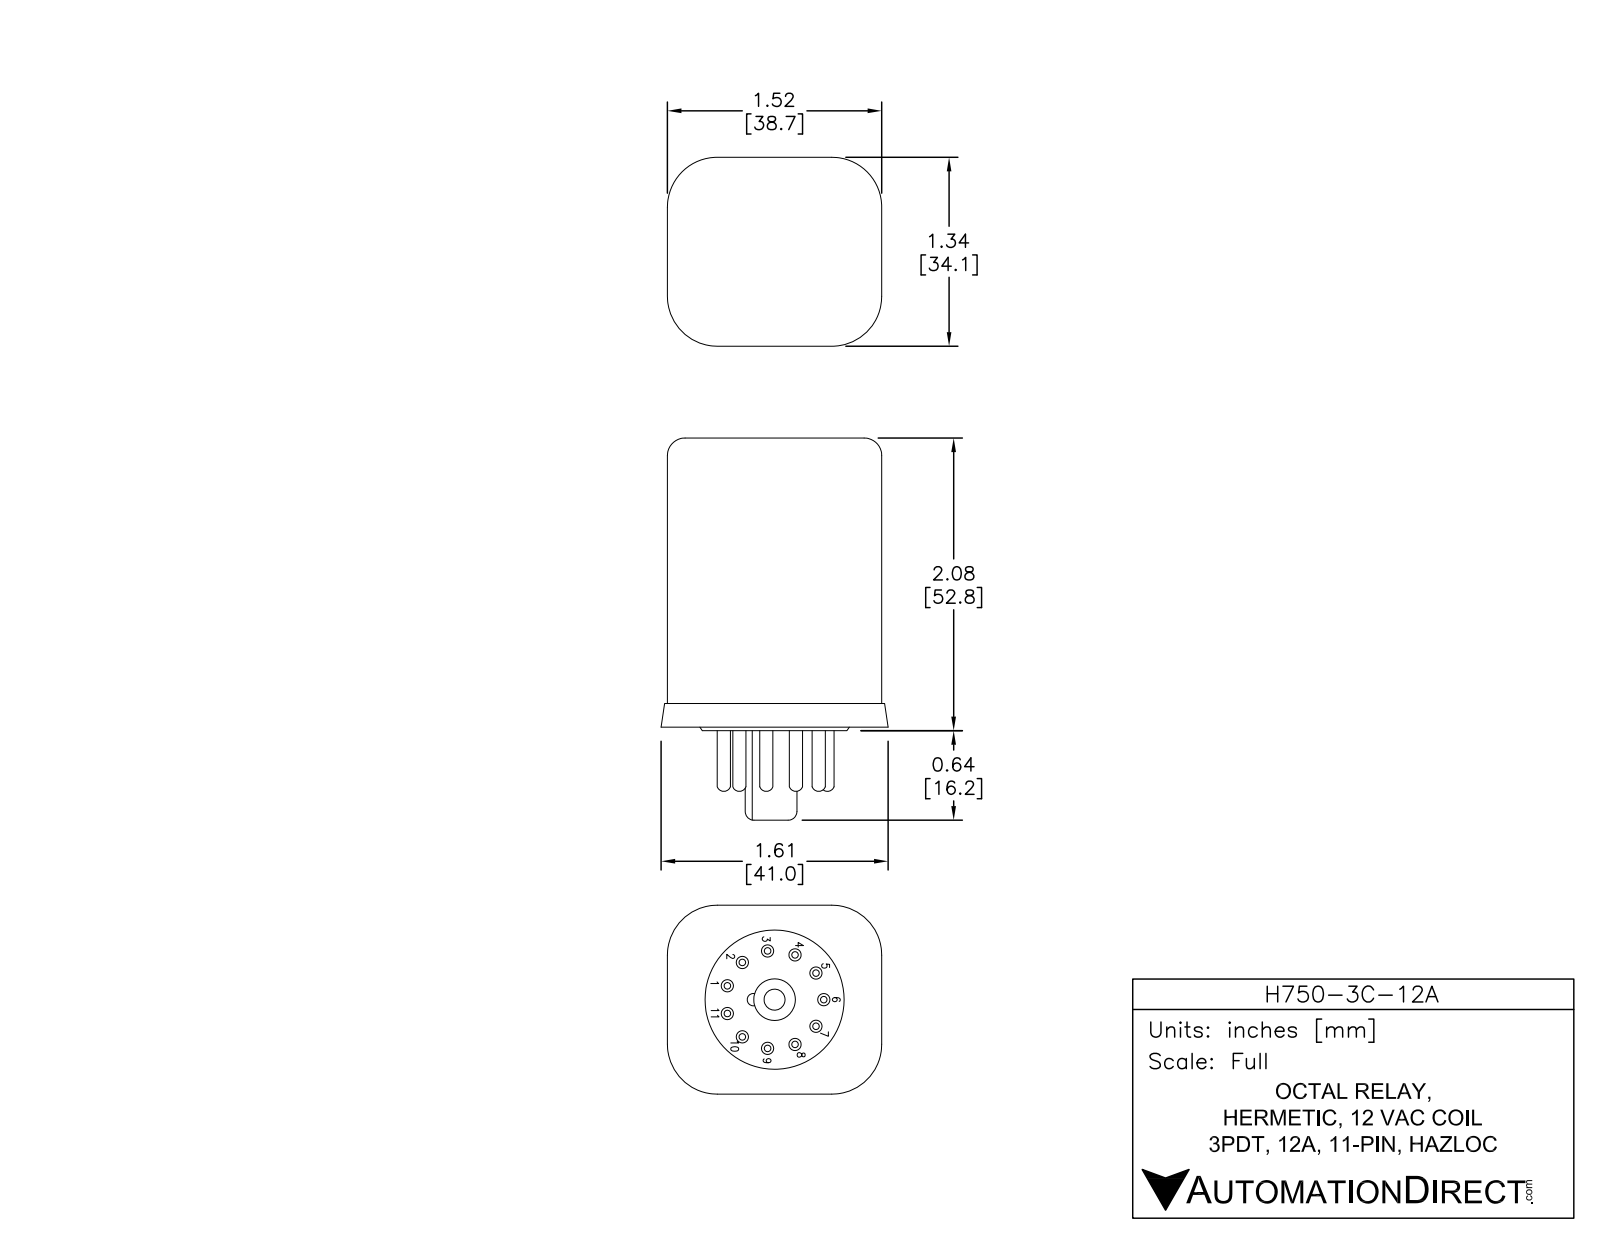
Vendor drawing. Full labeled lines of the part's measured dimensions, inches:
Part name (STEP PRODUCT): H750-3C-12A
STEP written by: SolidWorks 2013 (AUTOMOTIVE_DESIGN)
Units: inches
Bodies: 12 solids, 276 faces (121 planar, 65 cylindrical, 90 other)
Overall size (bounding box): 2.65 × 1.628 × 1.441
Volume: 4.086 in³ · Surface area: 16.65 in²
Round holes (diameter × count): ⌀0.177 ×8, ⌀0.154 ×1
Round bosses / shafts (diameter × count): ⌀0.091 ×8, ⌀1.063 ×1, ⌀0.472 ×1, ⌀0.315 ×1
Partial cylindrical surfaces — rounded edges, fillets, slot ends (radius × count): R0.024 ×8, R0.098 ×4, R0.394 ×4, R0.445 ×4, R0.02 ×2, R0.023 ×1
Main face-to-face distances: 2.087, 1.339, 1.526, 0.02, 2.106, 0.051, 1.39, 1.577, 0.039, 2.126
Hole centre spacings: 0.335, 0.473, 0.618, 0.256, 0.256, 0.669
